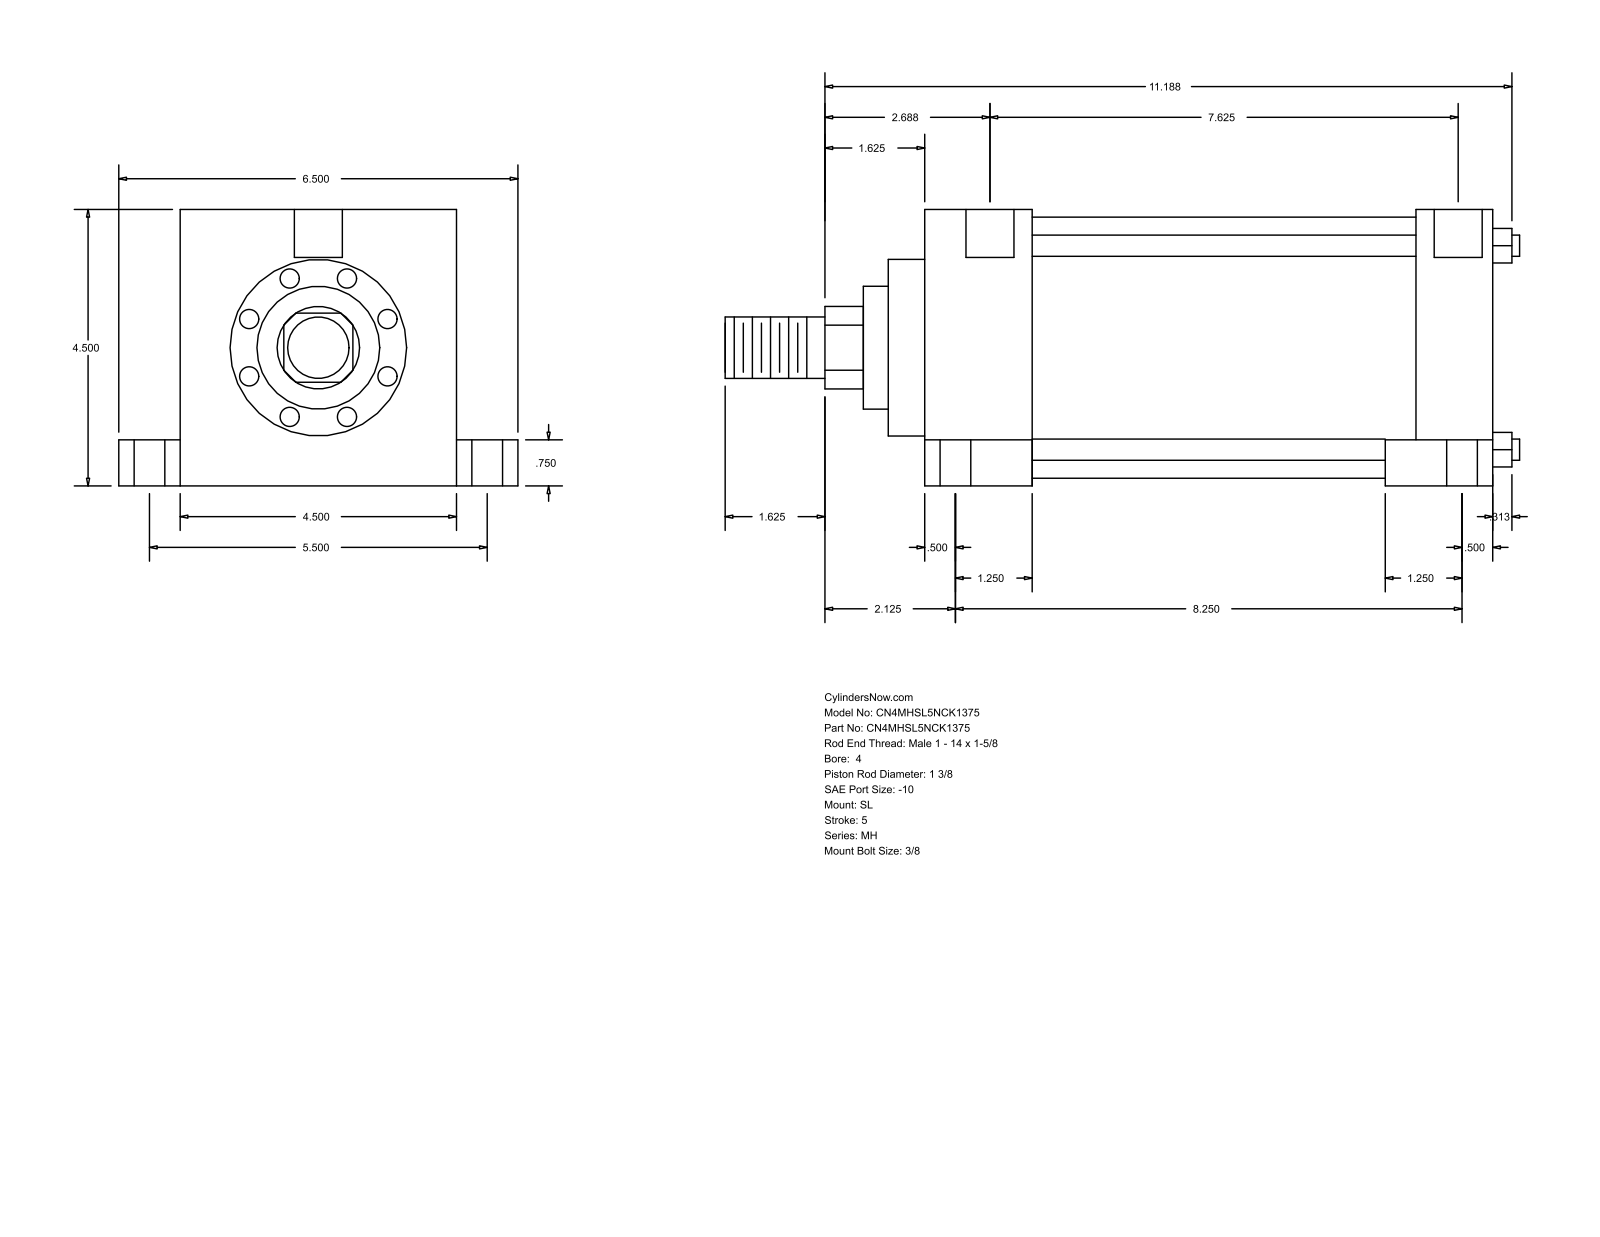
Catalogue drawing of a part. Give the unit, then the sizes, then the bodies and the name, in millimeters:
Units: millimetres
Overall size (bounding box): 328.61 × 165.1 × 114.3
Round holes (diameter × count): ⌀8.73 ×4, ⌀12.7 ×4, ⌀19.05 ×4, ⌀19.84 ×2
Round bosses / shafts (diameter × count): ⌀8.76 ×4, ⌀107.95 ×1, ⌀73.03 ×1, ⌀50.8 ×1, ⌀34.92 ×1, ⌀25.4 ×1
Partial cylindrical surfaces — rounded edges, fillets, slot ends (radius × count): R17.06 ×1
Main face-to-face distances: 114.3, 234.96, 44.45, 190.51, 203.2, 158.75, 31.76, 25.4, 139.7, 19.05
Hole centre spacings: 69.85, 69.87, 70.99, 71.29, 139.7, 196.85, 207.38, 208.88
Bodies: 0 solids, 110 faces (77 planar, 33 cylindrical, 0 other)
Part name (STEP PRODUCT): MH_SL__0400_1.375
STEP written by: GSSL Pune (CONFIG_CONTROL_DESIGN)
